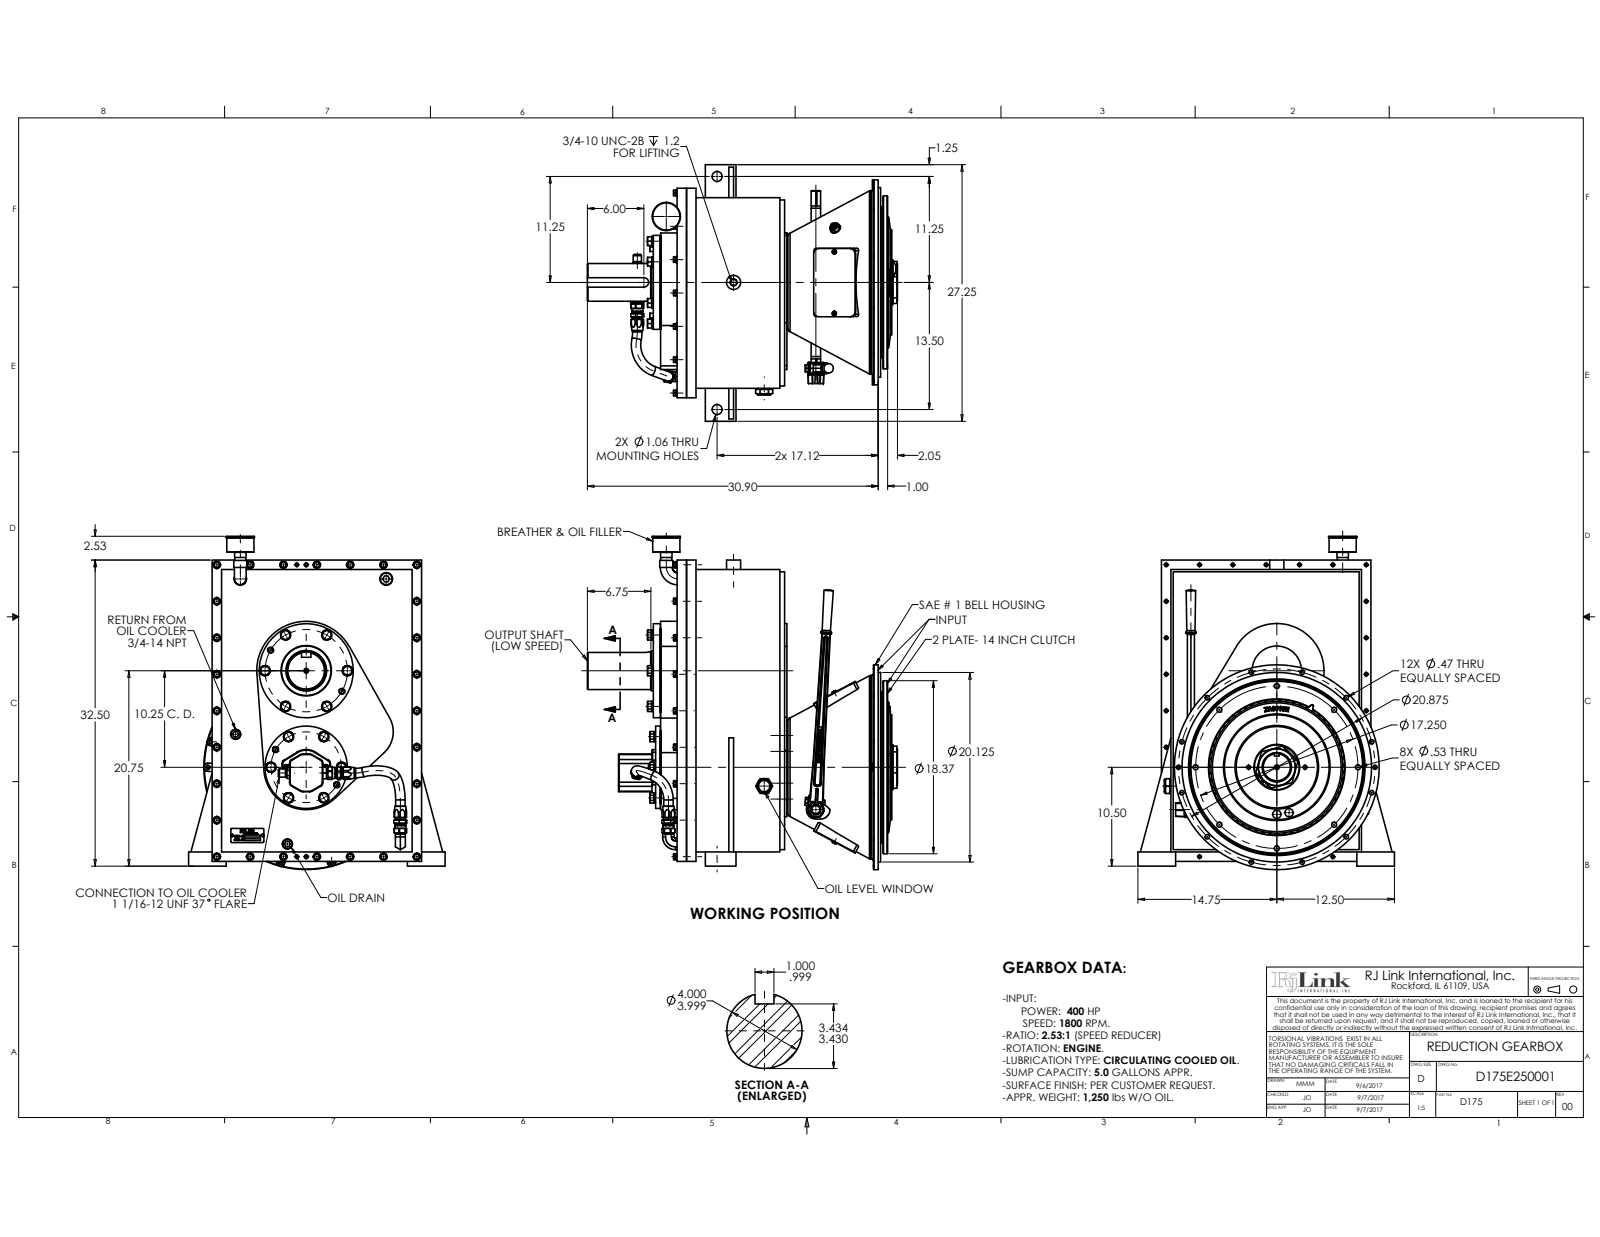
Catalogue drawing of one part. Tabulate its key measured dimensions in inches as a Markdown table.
| quantity | value |
| --- | --- |
| part name | SHCS_38-16X1_00_17; 30313_CONE_8; OS4_500X5_501-2_6; PPSKG_75-14_15 (+8 more) |
| STEP written by | SolidWorks 2017 (AUTOMOTIVE_DESIGN) |
| units | inches |
| bodies | 94 solids, 5468 faces (2183 planar, 2360 cylindrical, 925 other) |
| overall size | 35.405 × 32.885 × 27.25 |
| volume | 102.2 in³ |
| surface area | 9 920 in² |
| round holes (diameter × count) | 0.312 × 43, 0.382 × 34, 0.406 × 34, 0.781 × 28, 0.656 × 23, 0.531 × 22, 0.469 × 12, 0.636 × 12, 0.875 × 11, 0.203 × 8, 0.66 × 6, 0.969 × 6 |
| round bosses / shafts (diameter × count) | 0.375 × 38, 0.683 × 34, 0.561 × 34, 0.625 × 29, 0.375 × 17, 0.25 × 15, 1.079 × 12, 0.937 × 12 |
| partial cylindrical surfaces (radius × count) | 0.014 × 34, 0.037 × 28, 0.25 × 22, 0.31 × 20, 0.06 × 14, 0.023 × 12, 0.62 × 12, 0.5 × 8 |
| main face-to-face distances | 0.5, 0.75, 19.75, 10.79, 0.25, 1, 1.5, 10.54, 11.29, 29.5 |
| hole center spacings | 3.375, 7.551, 4.437, 2.268, 5.575, 7.75, 7.686, 3.875 |
